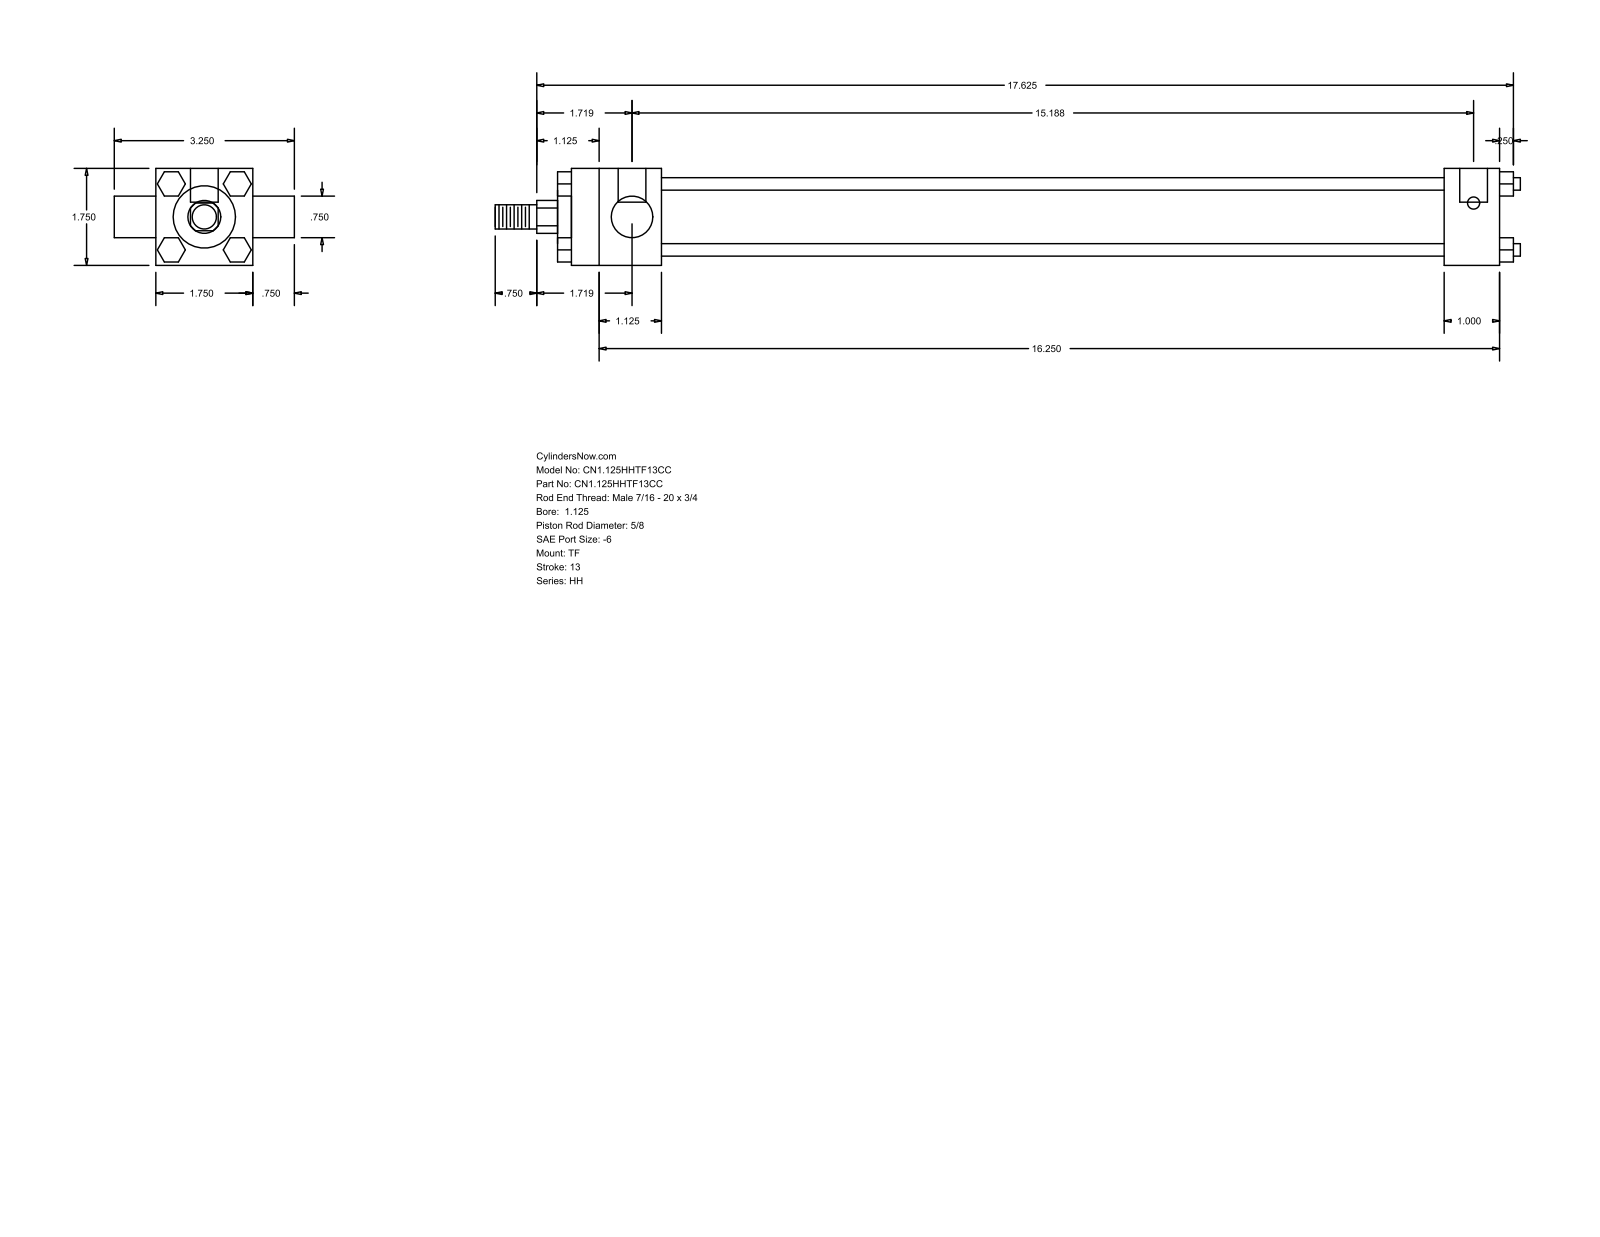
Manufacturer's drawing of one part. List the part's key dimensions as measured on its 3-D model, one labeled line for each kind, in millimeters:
Part name (STEP PRODUCT): HH_TF__0112_0.625
STEP written by: GSSL Pune (CONFIG_CONTROL_DESIGN)
Units: millimetres
Bodies: 0 solids, 120 faces (92 planar, 28 cylindrical, 0 other)
Overall size (bounding box): 469.9 × 82.55 × 44.45
Round holes (diameter × count): ⌀5.56 ×3, ⌀12.7 ×2
Round bosses / shafts (diameter × count): ⌀5.71 ×4, ⌀34.92 ×1, ⌀28.57 ×1, ⌀19.05 ×1, ⌀15.88 ×1, ⌀11.11 ×1
Partial cylindrical surfaces — rounded edges, fillets, slot ends (radius × count): R7.54 ×1
Main face-to-face distances: 44.46, 11.11, 358.78, 384.17, 25.39, 41.27, 400.05, 425.44, 47.62, 6.35
Hole centre spacings: 3.17, 382.59, 385.76
